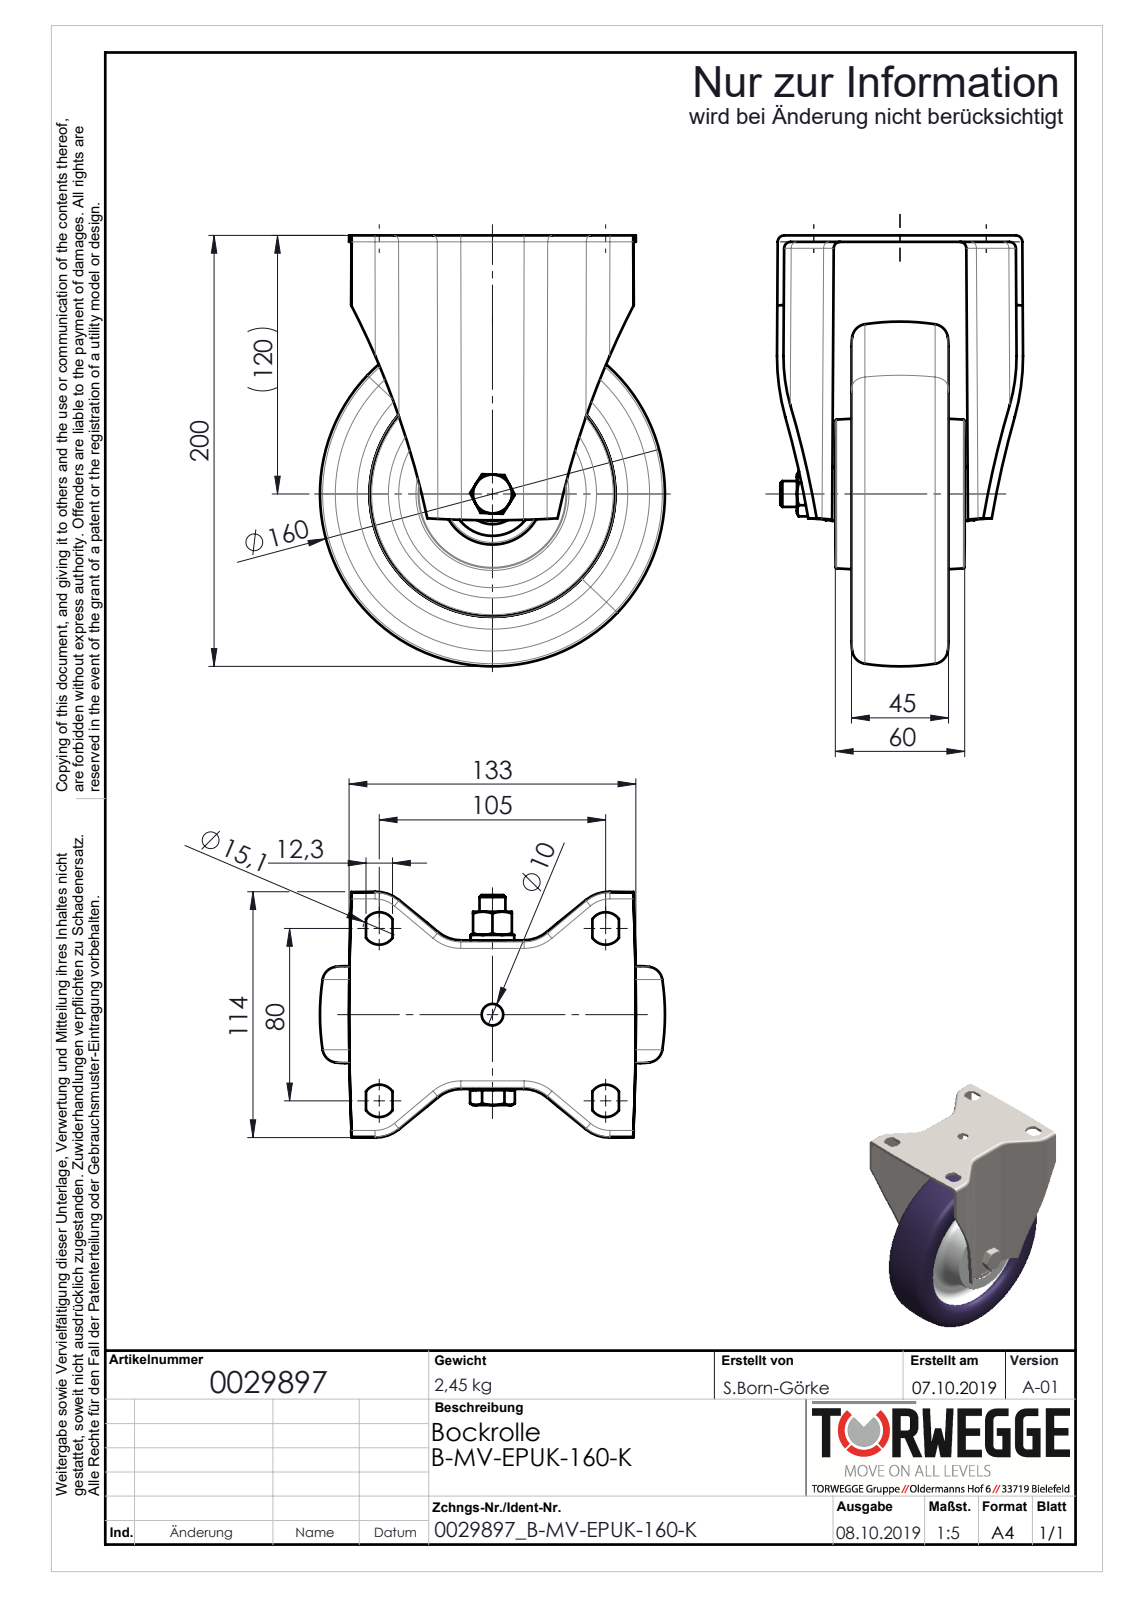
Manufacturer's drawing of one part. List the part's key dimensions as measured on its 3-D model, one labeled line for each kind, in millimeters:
Part name (STEP PRODUCT): 0029897_B-MV-EPUK-160-K_(A-01)
STEP written by: SolidWorks 2018 (AUTOMOTIVE_DESIGN)
Units: millimetres
Bodies: 11 solids, 514 faces (139 planar, 157 cylindrical, 218 other)
Overall size (bounding box): 200 × 160 × 114.1
Volume: 826 659 mm³ · Surface area: 255 388 mm²
Round holes (diameter × count): ⌀10 ×1, ⌀10.2 ×1, ⌀12 ×1, ⌀12.2 ×1, ⌀12.3 ×1, ⌀20 ×1, ⌀21 ×1, ⌀35 ×1, ⌀38.9 ×1
Round bosses / shafts (diameter × count): ⌀137 ×1, ⌀47 ×1, ⌀28.1 ×1, ⌀25 ×1, ⌀20.2 ×1, ⌀19.9 ×1, ⌀18 ×1
Partial cylindrical surfaces — rounded edges, fillets, slot ends (radius × count): R3 ×16, R17 ×8, R7.55 ×4, R14 ×4, R20 ×4, R400 ×2, R67.5 ×1, R501.25 ×1
Main face-to-face distances: 3, 1, 10, 12.5, 20, 22.5, 46, 11, 21, 23
